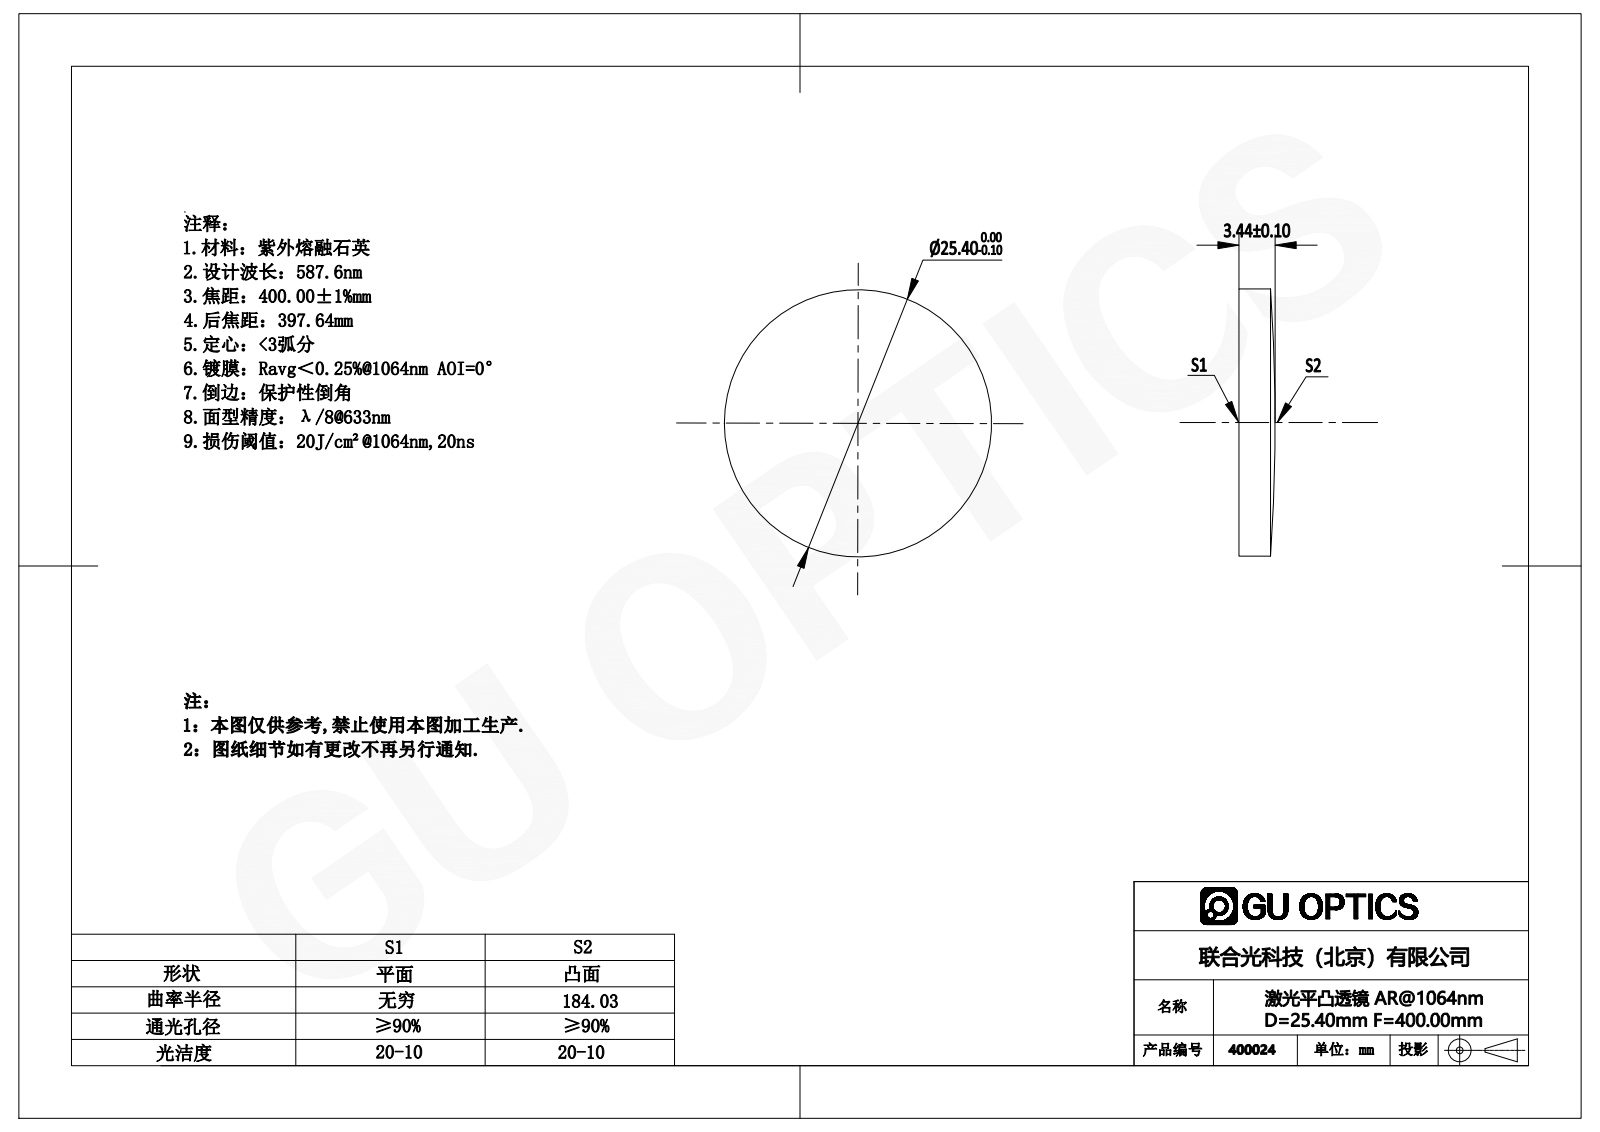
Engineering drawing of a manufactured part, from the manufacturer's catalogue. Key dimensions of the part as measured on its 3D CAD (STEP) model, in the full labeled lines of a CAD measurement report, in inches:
Part name (STEP PRODUCT): 400024
STEP written by: SolidWorks 2016 (AUTOMOTIVE_DESIGN)
Units: inches
Bodies: 1 solid, 5 faces (1 planar, 2 cylindrical, 2 other)
Overall size (bounding box): 1 × 1 × 0.135
Volume: 0.1 in³ · Surface area: 1.942 in²
Round bosses / shafts (diameter × count): ⌀1 ×1
